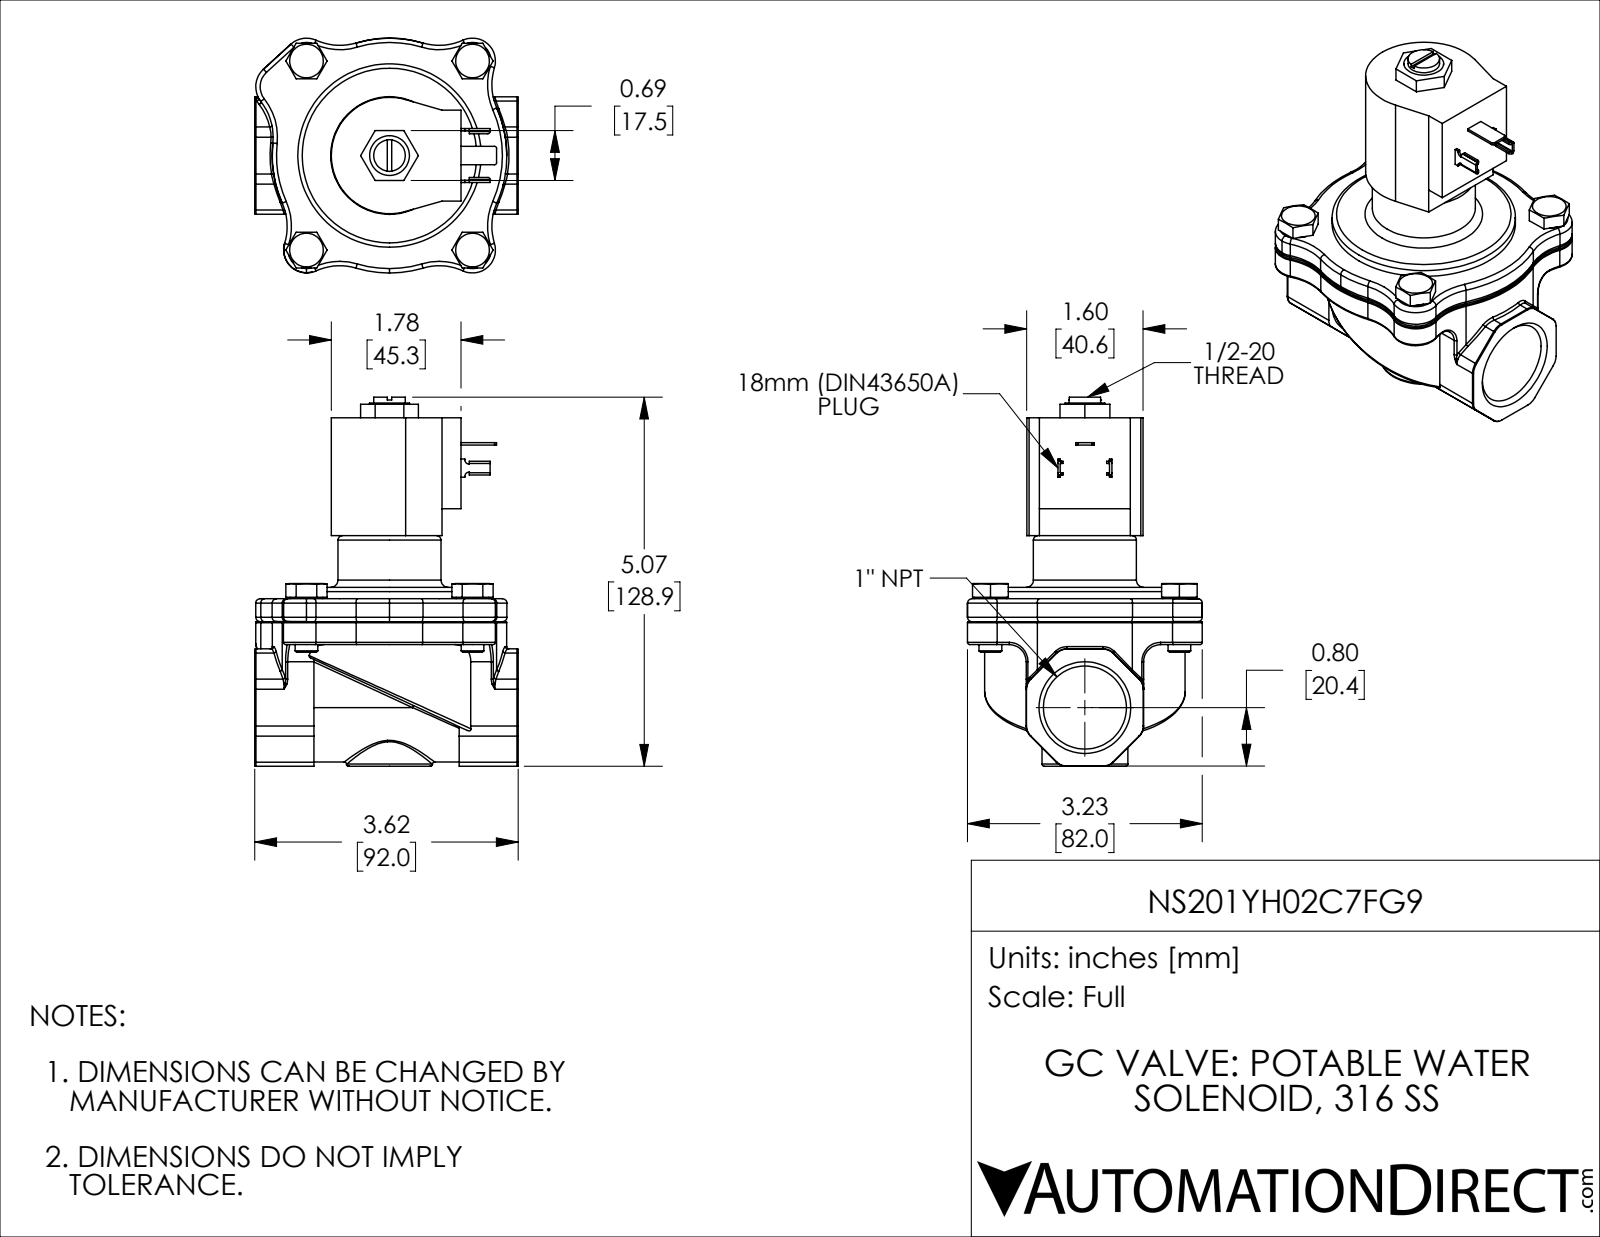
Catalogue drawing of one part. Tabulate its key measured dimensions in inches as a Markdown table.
| quantity | value |
| --- | --- |
| part name | NS201YH02C7FG9 |
| STEP written by | SolidWorks 2024 (CONFIG_CONTROL_DESIGN) |
| units | inches |
| bodies | 12 solids, 603 faces (162 planar, 221 cylindrical, 220 other) |
| overall size | 5.073 × 3.622 × 3.228 |
| volume | 18.69 in³ |
| surface area | 102.4 in² |
| round holes (diameter × count) | 0.25 × 4, 0.313 × 4, 0.125 × 1, 0.236 × 1, 0.488 × 1, 0.504 × 1, 0.949 × 1, 1.141 × 1, 3 × 1 |
| round bosses / shafts (diameter × count) | 0.45 × 4, 0.313 × 4, 2.65 × 1, 2.52 × 1, 1.417 × 1, 1.181 × 1, 0.547 × 1, 0.434 × 1 |
| partial cylindrical surfaces (radius × count) | 0.031 × 26, 0.787 × 16, 0.03 × 8, 0.197 × 8, 0.315 × 6, 0.06 × 2, 0.236 × 2, 0.327 × 1 |
| main face-to-face distances | 0.315, 0.03, 0.345, 2.831, 2.801, 2.486, 0.157, 1.211, 1.181, 0.866 |
| hole center spacings | 2.598, 1.729, 2.283, 3.458, 1.728, 1.73, 2.274, 2.282 |
